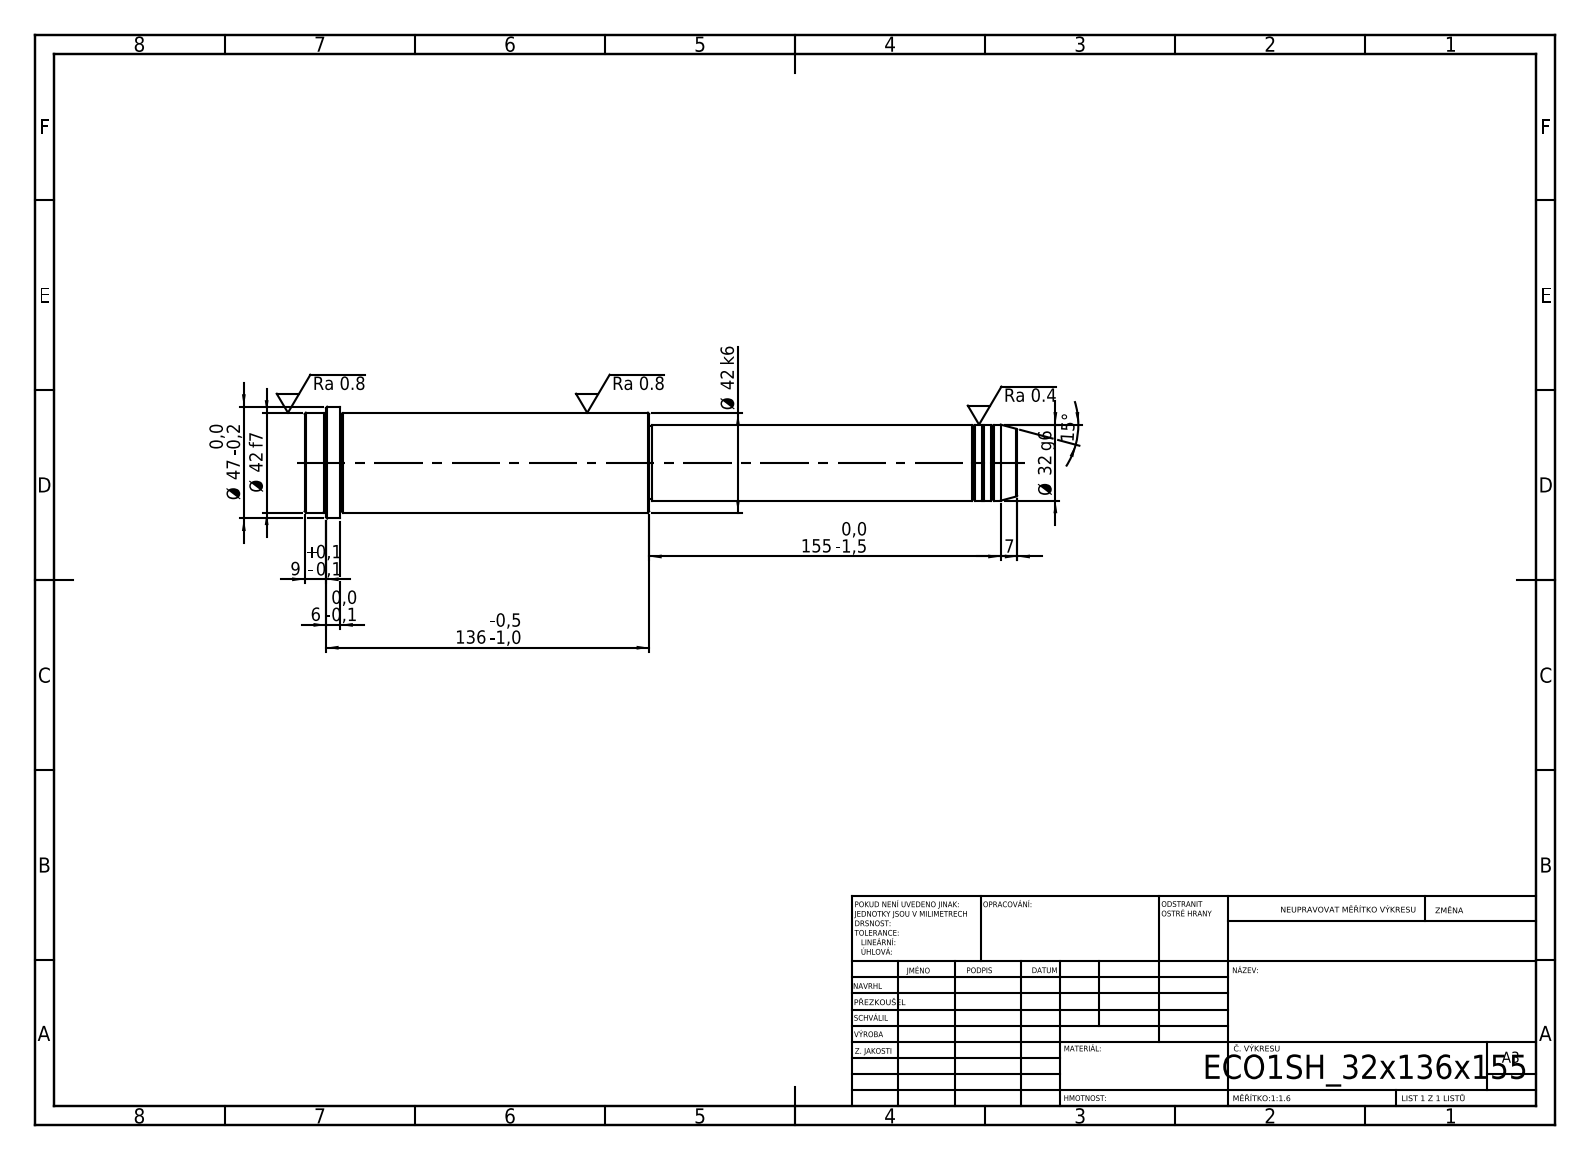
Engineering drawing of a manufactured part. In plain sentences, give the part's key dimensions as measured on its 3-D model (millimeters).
Its 3-D file was written by "SolidWorks 2019 (CONFIG_CONTROL_DESIGN)". It is 1 solid with 52 faces: 6 planar, 16 cylindrical and 30 other. Overall it measures 300 by 47 by 47 millimeters. Its volume is 326 688 cubic millimeters and its surface area 38 355 square millimeters. Round bosses or shafts: 1 of diameter 47, 1 of diameter 42, 1 of diameter 32, 1 of diameter 31. The main face-to-face distances are 300, 155, 145, 285, 130, 15, 291, 136, 6, 9.
